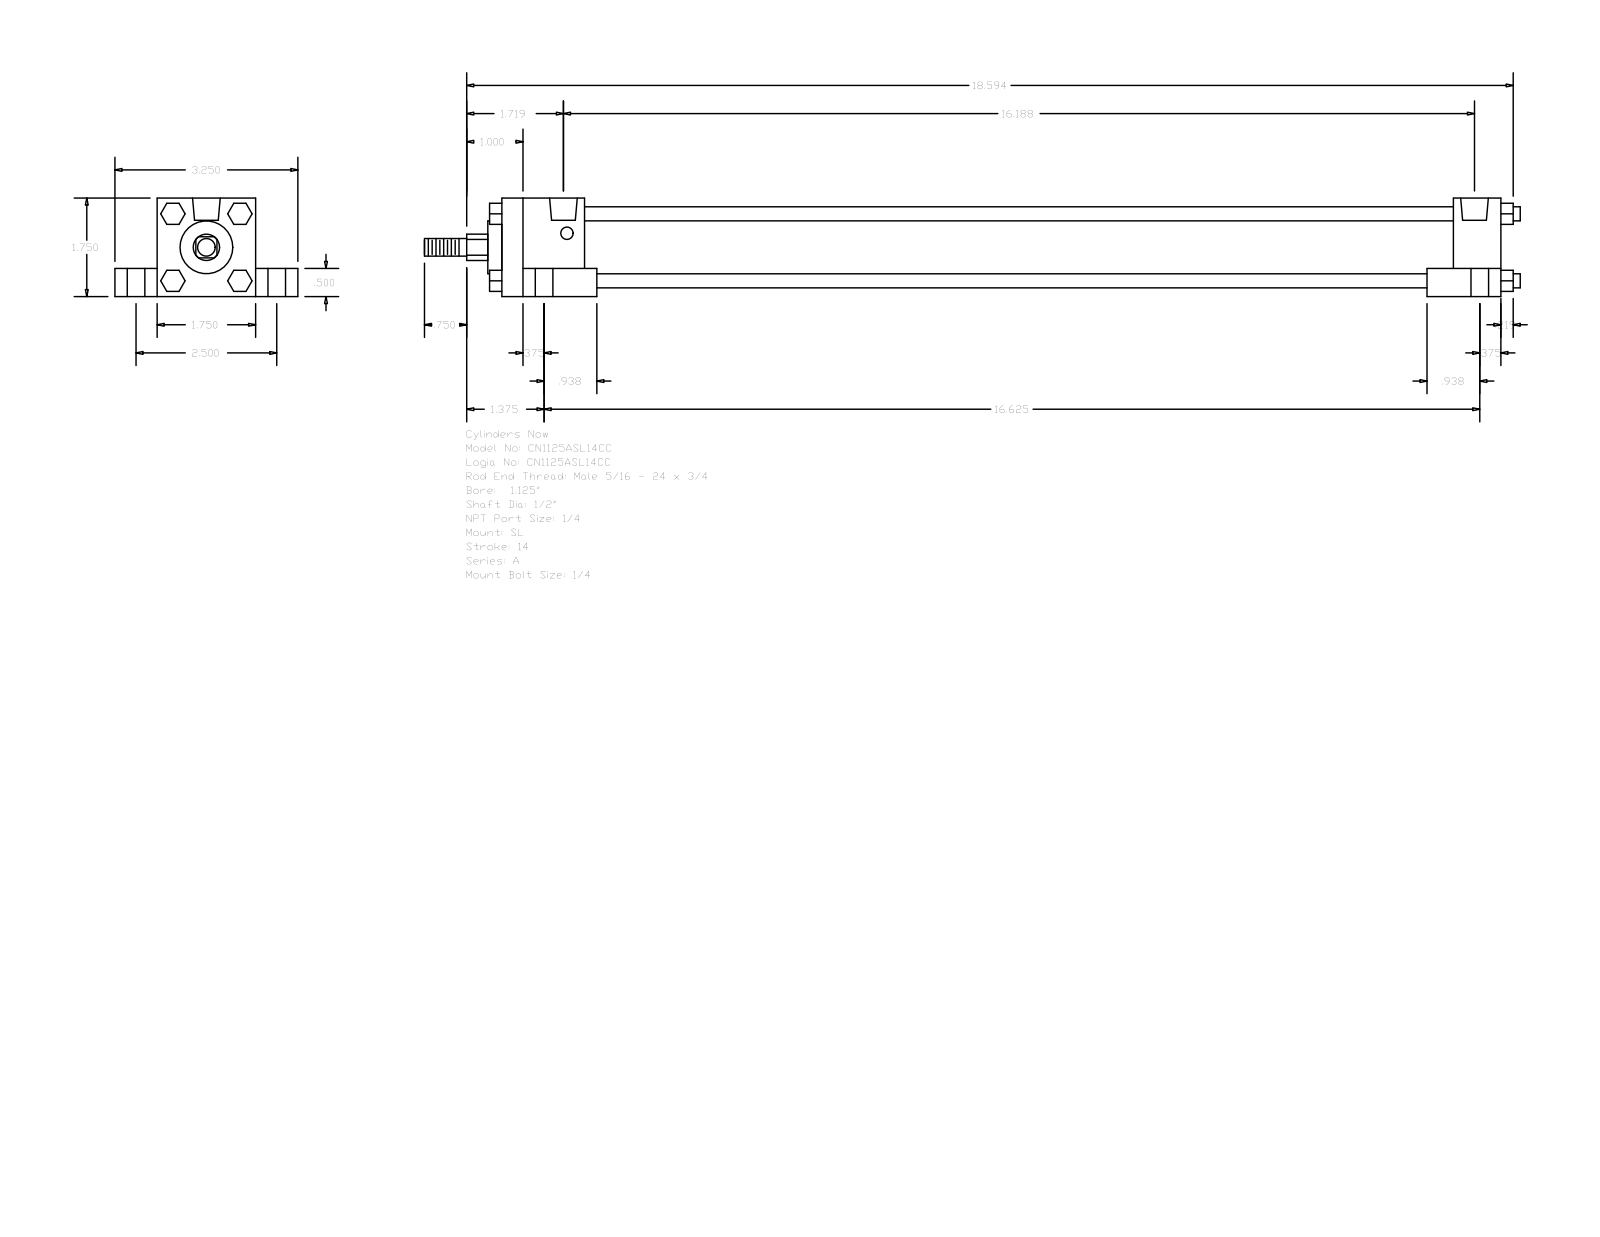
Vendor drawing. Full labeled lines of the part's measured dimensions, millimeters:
Part name (STEP PRODUCT): A_SL__0112_0.5
STEP written by: GSSL Pune (CONFIG_CONTROL_DESIGN)
Units: millimetres
Bodies: 0 solids, 150 faces (114 planar, 36 cylindrical, 0 other)
Overall size (bounding box): 494.51 × 82.55 × 44.45
Round holes (diameter × count): ⌀5.56 ×4, ⌀7.94 ×4, ⌀14.29 ×4, ⌀12.49 ×2
Round bosses / shafts (diameter × count): ⌀6.35 ×4, ⌀31.88 ×1, ⌀23.81 ×1, ⌀12.7 ×1, ⌀7.94 ×1
Partial cylindrical surfaces — rounded edges, fillets, slot ends (radius × count): R5.94 ×1
Main face-to-face distances: 44.46, 31.76, 12.7, 19.04, 63.5, 450.85, 429.41, 21.44, 37.3, 392.11
Hole centre spacings: 31.84, 32, 32.93, 33.39, 63.5, 407.99, 413.18, 414.76
